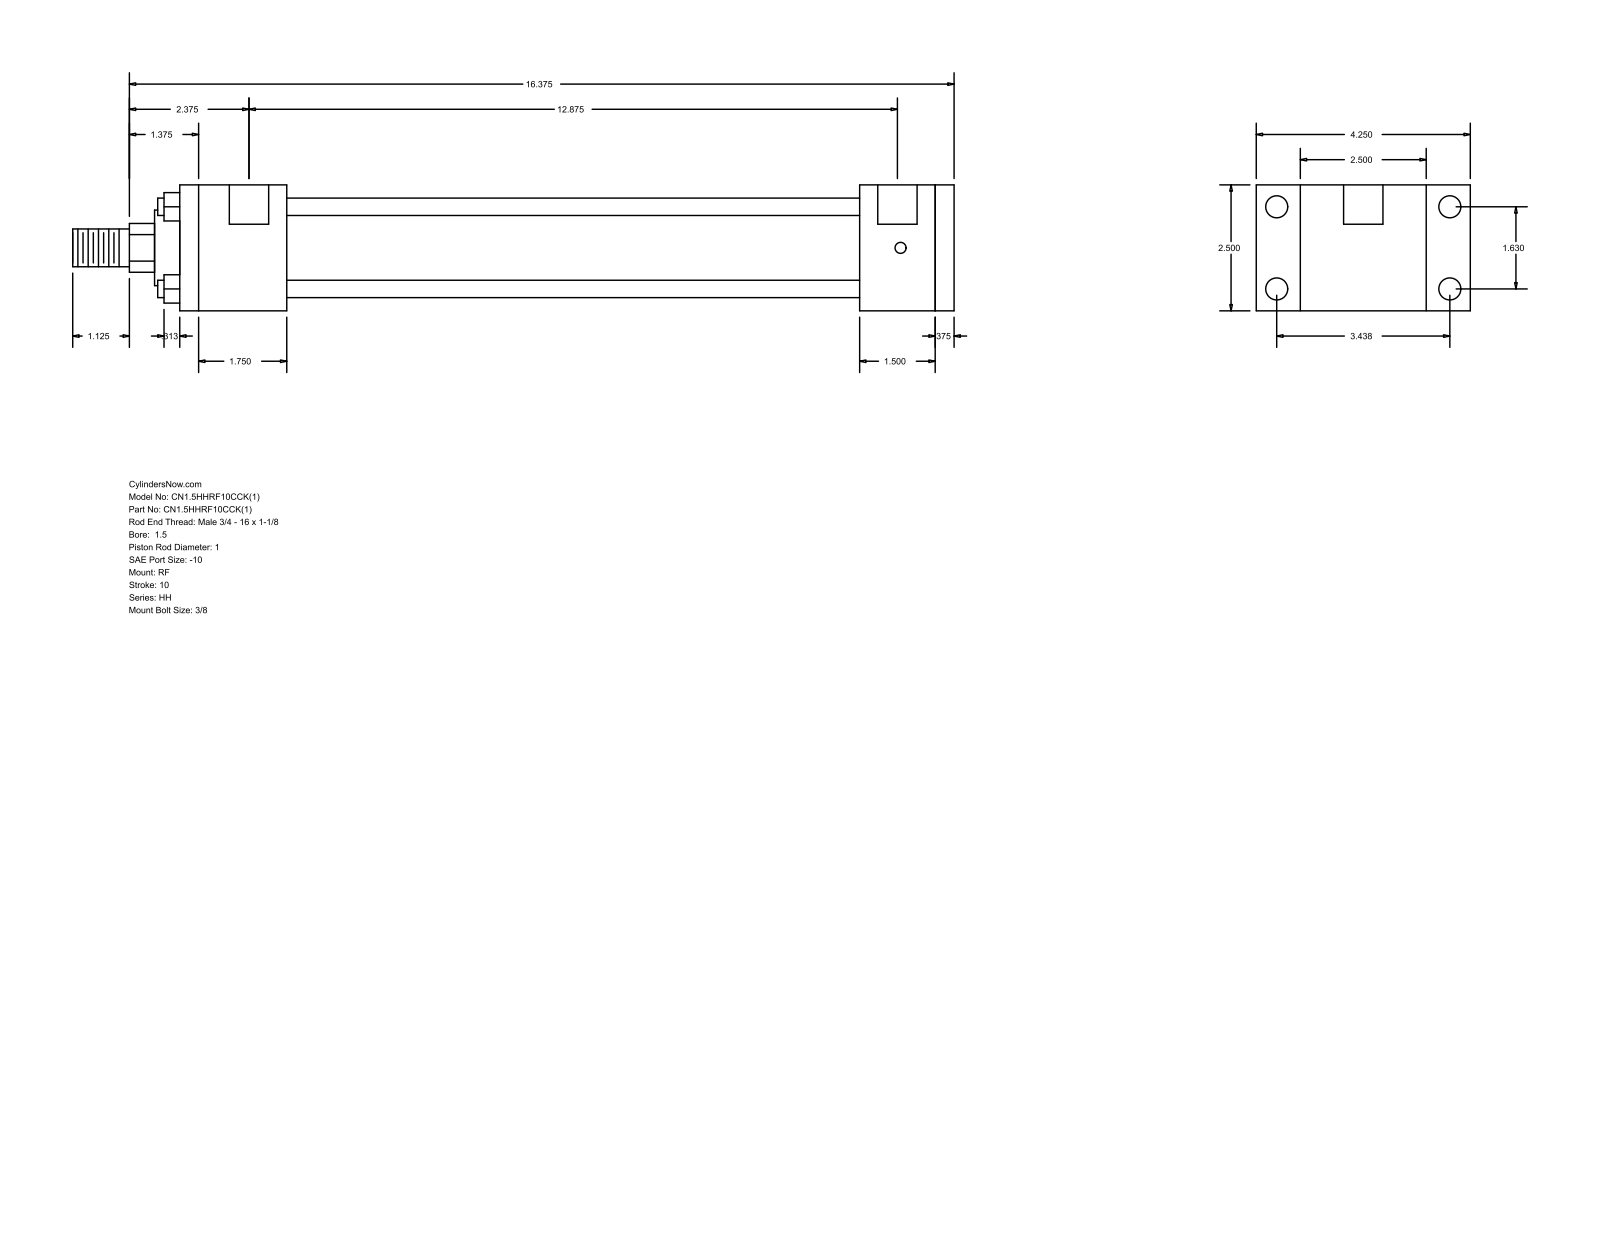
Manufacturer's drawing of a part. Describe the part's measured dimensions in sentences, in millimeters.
The part is named "HH_RF__0150_1". Its 3-D file was written by "GSSL Pune (CONFIG_CONTROL_DESIGN)". It is 0 solids with 92 faces: 64 planar, 28 cylindrical and 0 other. Overall it measures 444.5 by 107.95 by 63.5 millimeters. Round holes: 4 of diameter 5.56, 4 of diameter 11.13, 2 of diameter 19.84. Round bosses or shafts: 4 of diameter 8.76, 1 of diameter 44.45, 1 of diameter 38.1, 1 of diameter 25.4, 1 of diameter 19.05. Partial cylindrical surfaces (rounded edges, fillets, slot ends): 1 of radius 12.29. The main face-to-face distances are 63.5, 9.53, 38.1, 288.92, 327.02, 336.55, 47.63, 53.98, 342.9, 381. The hole center spacings are 1.59, 41.4, 87.32, 96.64, 328.61, 330.2, 327.02.
